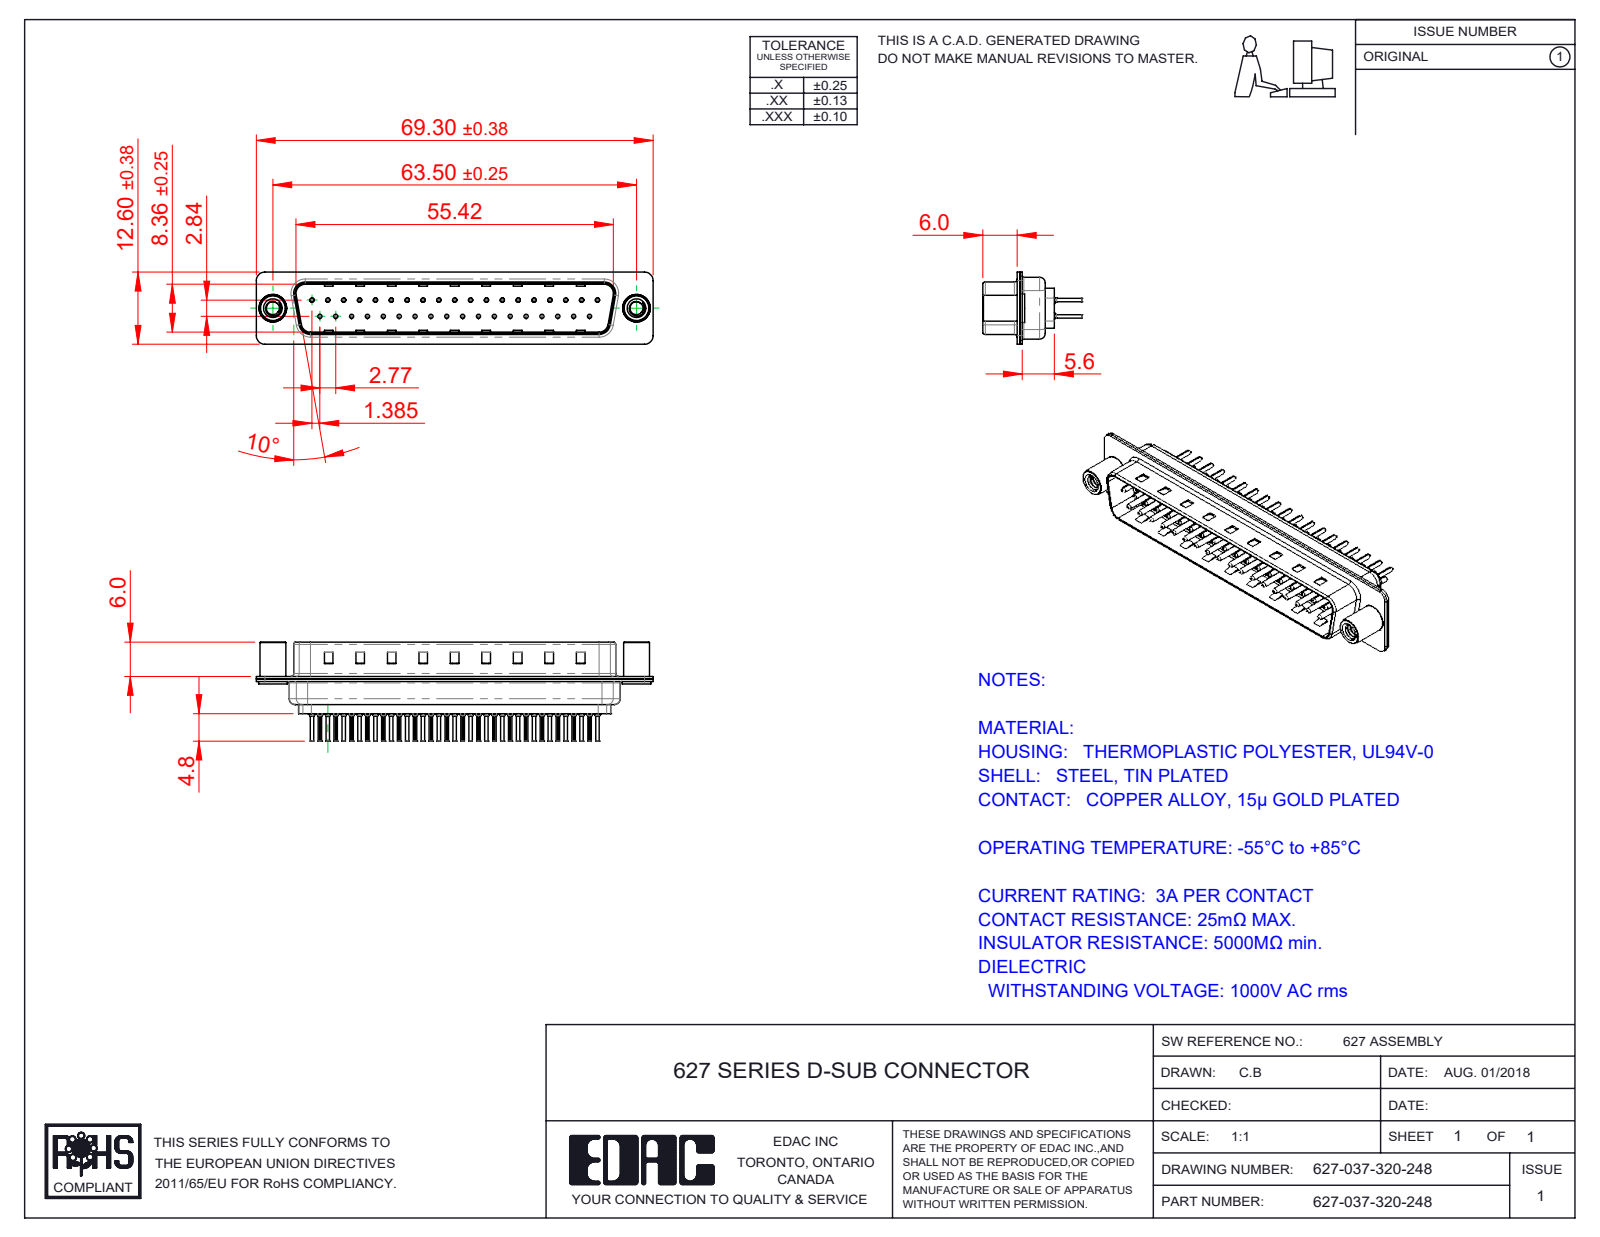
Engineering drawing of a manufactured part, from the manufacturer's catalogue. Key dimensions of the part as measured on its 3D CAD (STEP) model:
Part name (STEP PRODUCT): 627 Contact Row 2_20L; 627 Shell Front_37 Contacts; 627 Housing_37 LP; 627 4-40 Threaded Standoff (+3 more)
STEP written by: SolidWorks 2020 (CONFIG_CONTROL_DESIGN)
Units: millimetres
Bodies: 42 solids, 4072 faces (1093 planar, 1538 cylindrical, 1441 other)
Overall size (bounding box): 69.3 × 17.3 × 12.6
Volume: 3 765 mm³ · Surface area: 10 875 mm²
Round holes (diameter × count): ⌀0.2 ×37, ⌀0.35 ×37, ⌀1.1 ×37, ⌀1.6 ×37, ⌀2.26 ×2, ⌀4 ×2, ⌀4.8 ×2
Round bosses / shafts (diameter × count): ⌀2 ×37, ⌀1.5 ×37, ⌀0.75 ×37, ⌀0.6 ×37, ⌀5 ×2, ⌀4.9 ×2, ⌀4.5 ×2
Partial cylindrical surfaces — rounded edges, fillets, slot ends (radius × count): R0.1 ×74, R1.5 ×16, R2 ×12, R0.5 ×8, R1.6 ×8, R0.25 ×4, R0.6 ×4, R0.65 ×4
Main face-to-face distances: 0.4, 0.82, 9.58, 0.45, 8.76, 1.5, 0.9, 1.4, 6.05, 0.42
Hole centre spacings: 3.16, 2.77, 5.54, 8.31, 5.04, 10.1, 11.08, 12.78
